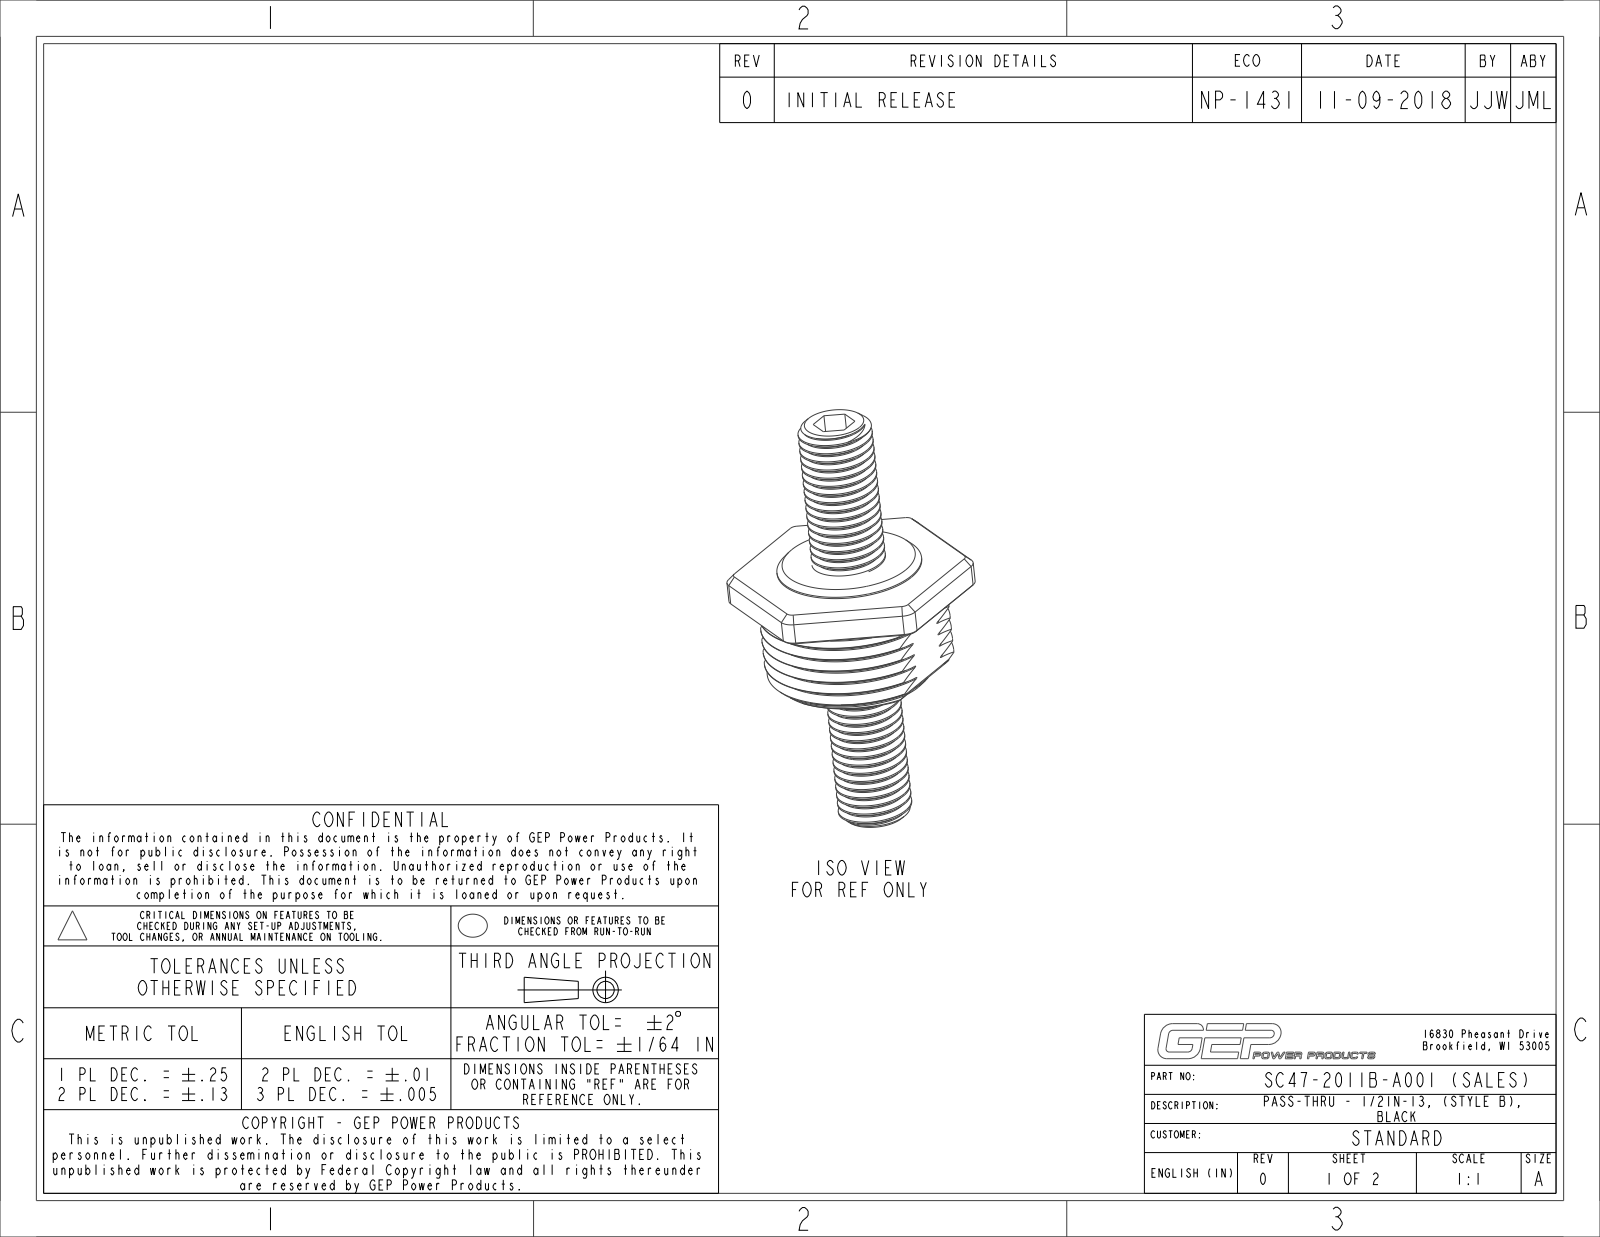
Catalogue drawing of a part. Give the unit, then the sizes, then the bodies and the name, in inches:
Units: inches
Overall size (bounding box): 3 × 1.701 × 1.5
Round holes (diameter × count): ⌀0.422 ×1
Round bosses / shafts (diameter × count): ⌀1 ×1, ⌀0.51 ×1
Partial cylindrical surfaces — rounded edges, fillets, slot ends (radius × count): R0.1 ×6, R0.181 ×6, R0.03 ×2, R0.652 ×1
Main face-to-face distances: 0.05, 0.85, 0.25, 0.2, 0.65, 0.9, 0.875, 0.625, 0.6, 1.5
Volume: 1.48 in³ · Surface area: 15.28 in²
Bodies: 1 solid, 289 faces (43 planar, 106 cylindrical, 140 other)
Part name (STEP PRODUCT): SC47-2011B-A001_NCF_SW0001
STEP written by: CREO PARAMETRIC BY PTC INC, 2017110 (CONFIG_CONTROL_DESIGN)
